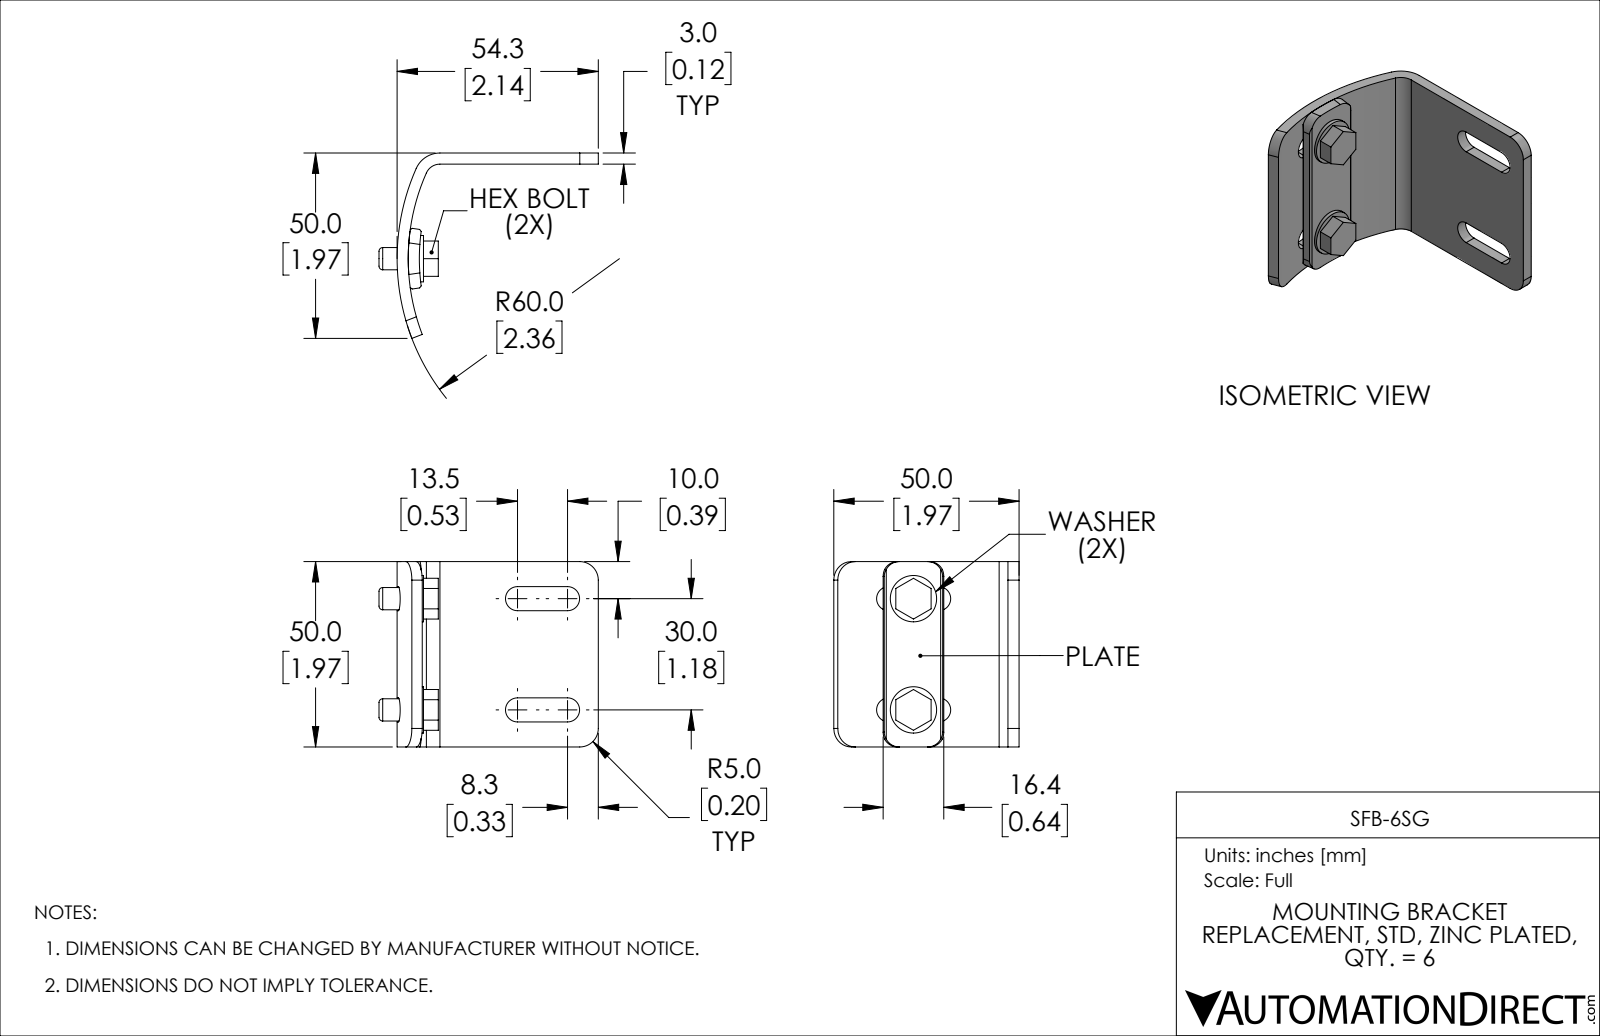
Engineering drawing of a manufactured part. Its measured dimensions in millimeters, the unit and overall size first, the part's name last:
Units: millimetres
Overall size (bounding box): 2675.7 × 1510.4 × 500
Round holes (diameter × count): ⌀64 ×4, ⌀65 ×4, ⌀125 ×4
Round bosses / shafts (diameter × count): ⌀60 ×4
Partial cylindrical surfaces — rounded edges, fillets, slot ends (radius × count): R40 ×30, R32.5 ×20, R50 ×18, R570 ×12, R70 ×6, R540 ×6, R600 ×6
Main face-to-face distances: 1010.4, 30, 1040.4, 980.4, 1039.9, 500, 1024.2, 2064, 16, 59.9
Hole centre spacings: 300, 1010.4, 1054
Volume: 98 190 000 mm³ · Surface area: 8 037 000 mm²
Bodies: 36 solids, 480 faces (276 planar, 192 cylindrical, 12 other)
Part name (STEP PRODUCT): SFB-6SG - 1; WebAssembly
STEP written by: SolidWorks 2019 (AUTOMOTIVE_DESIGN)
